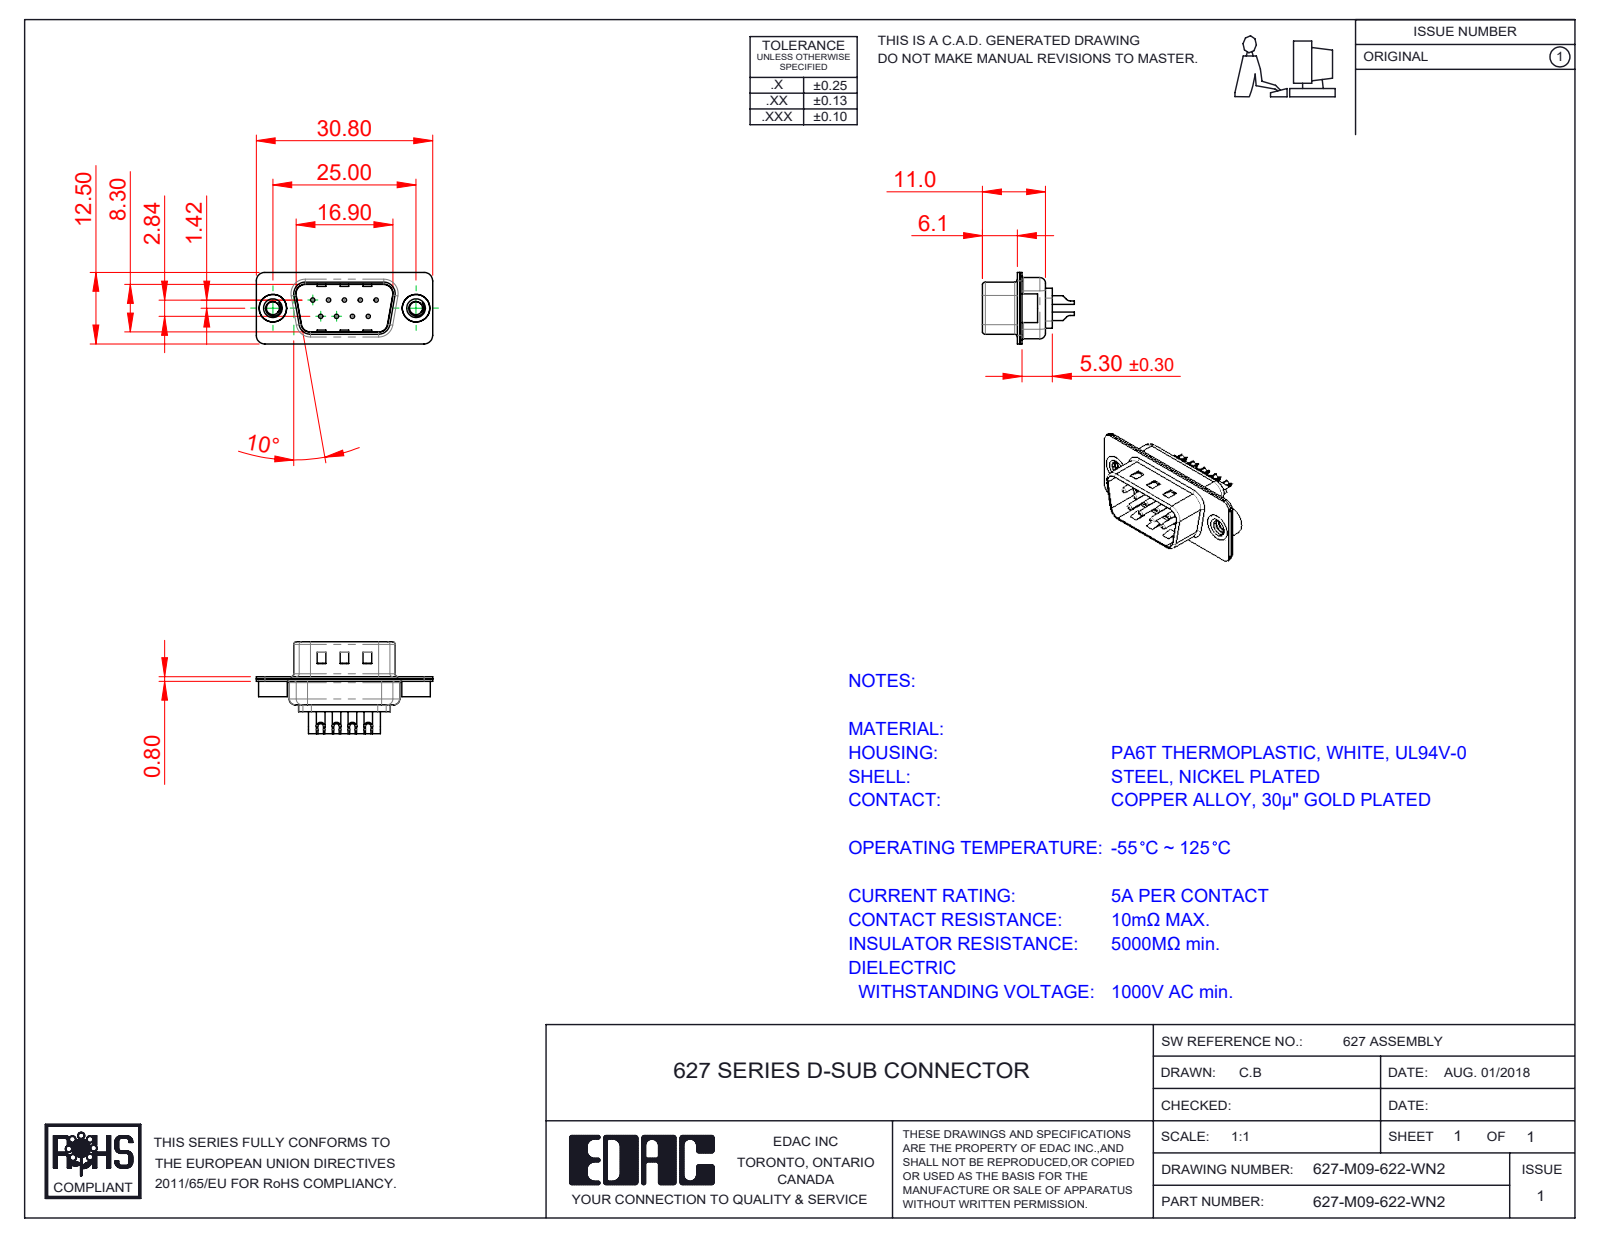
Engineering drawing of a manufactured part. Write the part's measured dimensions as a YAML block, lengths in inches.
part_name: "627M Contact Row 1_22; 627-M09-622-WN2; 627M Shell Front_09 Contacts; 627M Contact Row 2_22 (+3 more)"
step_written_by: "SolidWorks 2020 (CONFIG_CONTROL_DESIGN)"
units: inches
bodies: {solids: 14, faces: 637, planar: 188, cylindrical: 273, other: 176}
overall_size: [1.213, 0.632, 0.492]
volume: 0.081
surface_area: 5.67
round_holes:
  - {diameter: 0.03, count: 9}
  - {diameter: 0.039, count: 9}
  - {diameter: 0.063, count: 9}
  - {diameter: 0.079, count: 9}
  - {diameter: 0.089, count: 2}
  - {diameter: 0.157, count: 2}
  - {diameter: 0.189, count: 2}
round_bosses_or_shafts:
  - {diameter: 0.059, count: 9}
  - {diameter: 0.197, count: 2}
  - {diameter: 0.193, count: 2}
partial_cylinders:
  - {radius: 0.059, count: 16}
  - {radius: 0.079, count: 12}
  - {radius: 0.02, count: 8}
  - {radius: 0.063, count: 8}
  - {radius: 0.039, count: 6}
  - {radius: 0.01, count: 4}
  - {radius: 0.024, count: 4}
  - {radius: 0.026, count: 4}
face_to_face_distances: [0.016, 0.031, 0.374, 0.358, 0.343, 0.026, 0.39, 0.047, 0.03, 0.014]
hole_center_spacings: [0.124, 0.109, 0.218, 0.198, 0.198, 0.327, 0.28, 0.294]
